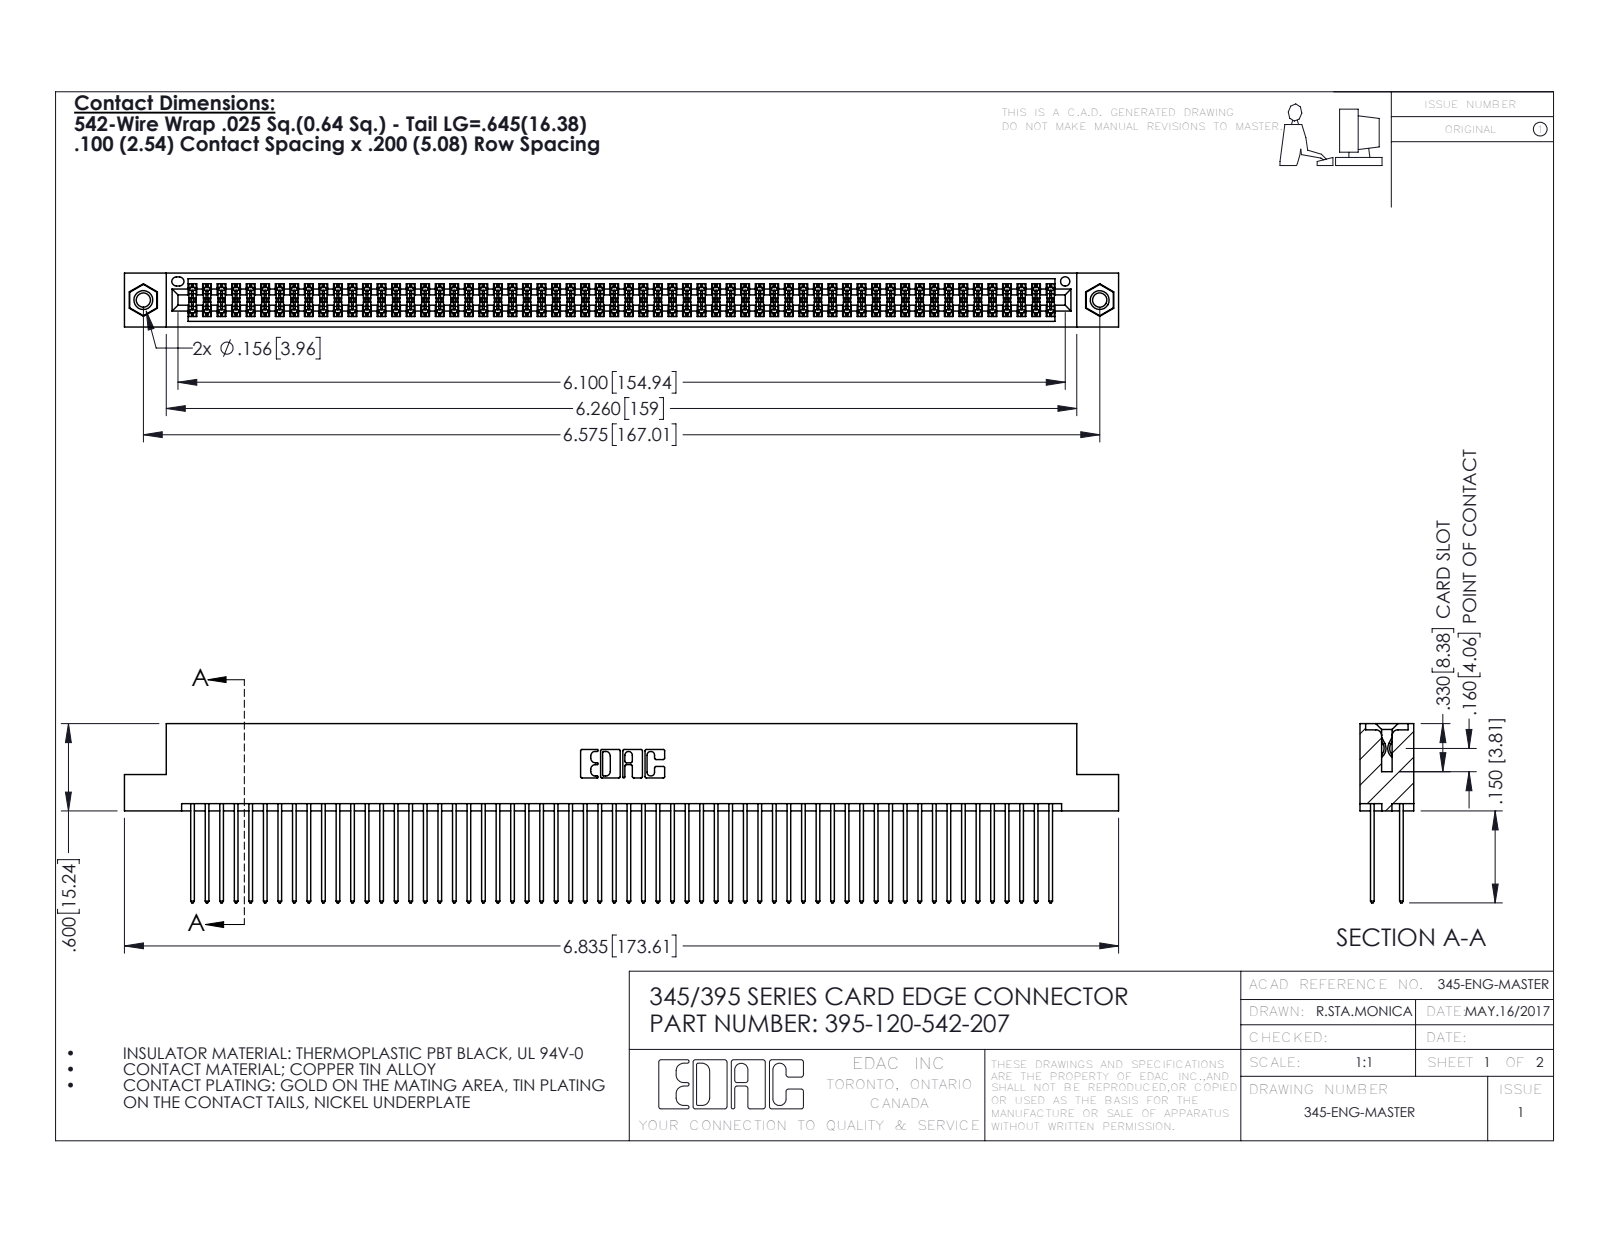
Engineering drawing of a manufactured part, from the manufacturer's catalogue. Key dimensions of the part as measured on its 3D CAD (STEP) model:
Part name (STEP PRODUCT): 345 Part_Flush Mounting Lugs - 0.156 Dia-TI; 345-250-001_345-250-005-103; 345-292-001_345-293-142; 395-120-542-207
STEP written by: SolidWorks 2016 (CONFIG_CONTROL_DESIGN)
Units: inches
Bodies: 123 solids, 6186 faces (4072 planar, 2098 cylindrical, 16 other)
Overall size (bounding box): 6.835 × 1.232 × 0.37
Volume: 1.073 in³ · Surface area: 44.91 in²
Round holes (diameter × count): ⌀0.098 ×2, ⌀0.125 ×2, ⌀0.156 ×2, ⌀0.064 ×1
Round bosses / shafts (diameter × count): ⌀0.155 ×2
Partial cylindrical surfaces — rounded edges, fillets, slot ends (radius × count): R0.006 ×180, R0.01 ×120, R0.01 ×22, R0.007 ×6, R0.031 ×6, R0.026 ×3, R0.014 ×2, R0.019 ×2
Main face-to-face distances: 0.072, 0.298, 0.2, 0.098, 0.272, 0.025, 0.225, 0.37, 0.175, 0.149
Hole centre spacings: 0.27, 6.339, 6.575
